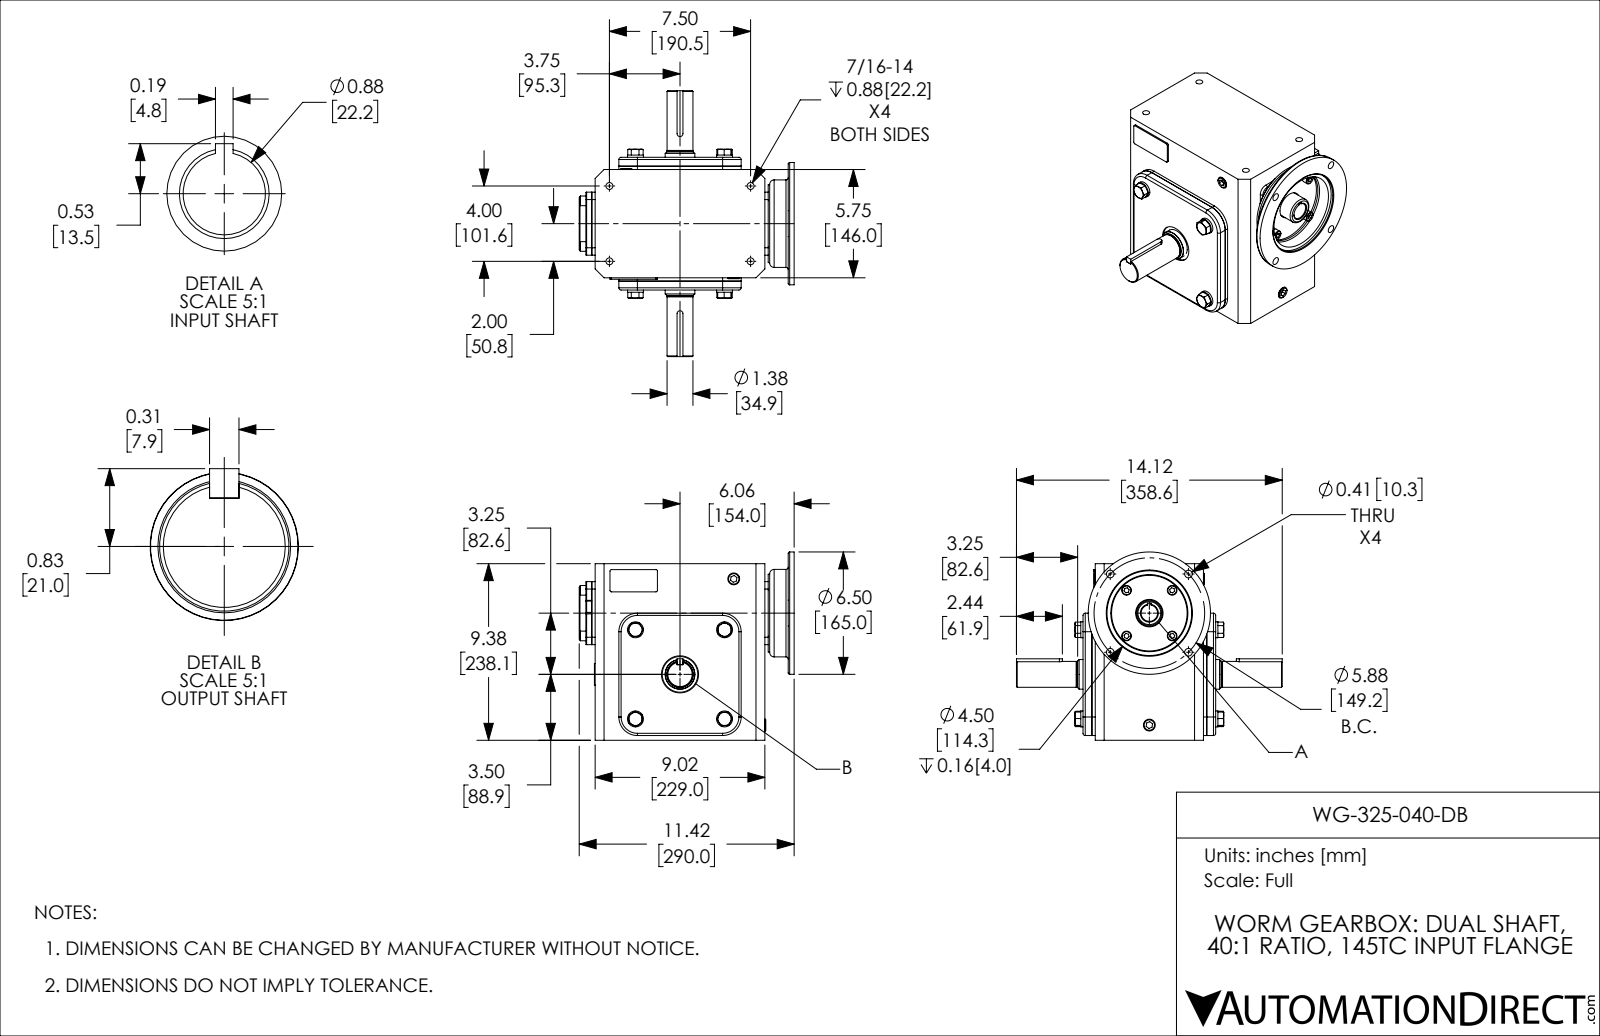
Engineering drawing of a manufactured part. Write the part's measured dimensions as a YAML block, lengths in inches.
part_name: "WG-325-040-DB"
step_written_by: "SolidWorks 2017 (AUTOMOTIVE_DESIGN)"
units: inches
bodies: {solids: 42, faces: 612, planar: 331, cylindrical: 178, other: 103}
overall_size: [14.118, 11.417, 9.998]
volume: 516.3
surface_area: 941.7
round_holes:
  - {diameter: 0.368, count: 4}
  - {diameter: 0.406, count: 4}
  - {diameter: 0.628, count: 3}
  - {diameter: 0.591, count: 1}
  - {diameter: 0.875, count: 1}
  - {diameter: 0.978, count: 1}
  - {diameter: 1.181, count: 1}
  - {diameter: 1.457, count: 1}
  - {diameter: 1.969, count: 1}
  - {diameter: 2.441, count: 1}
  - {diameter: 2.756, count: 1}
  - {diameter: 4.016, count: 1}
round_bosses_or_shafts:
  - {diameter: 0.846, count: 4}
  - {diameter: 0.512, count: 4}
  - {diameter: 6.496, count: 1}
  - {diameter: 4.646, count: 1}
  - {diameter: 4.134, count: 1}
  - {diameter: 2.835, count: 1}
  - {diameter: 1.575, count: 1}
  - {diameter: 1.378, count: 1}
partial_cylinders:
  - {radius: 0.118, count: 8}
  - {radius: 0.079, count: 7}
  - {radius: 0.394, count: 4}
  - {radius: 0.906, count: 4}
  - {radius: 0.984, count: 4}
  - {radius: 0.02, count: 2}
  - {radius: 0.039, count: 2}
  - {radius: 0.156, count: 2}
face_to_face_distances: [0.079, 0.177, 6.496, 0.394, 6.969, 0.472, 6.575, 6.398, 0.571, 0.65]
hole_center_spacings: [2.937, 4.154, 2.385, 4, 4.389, 5.718, 5.817, 5.875]
